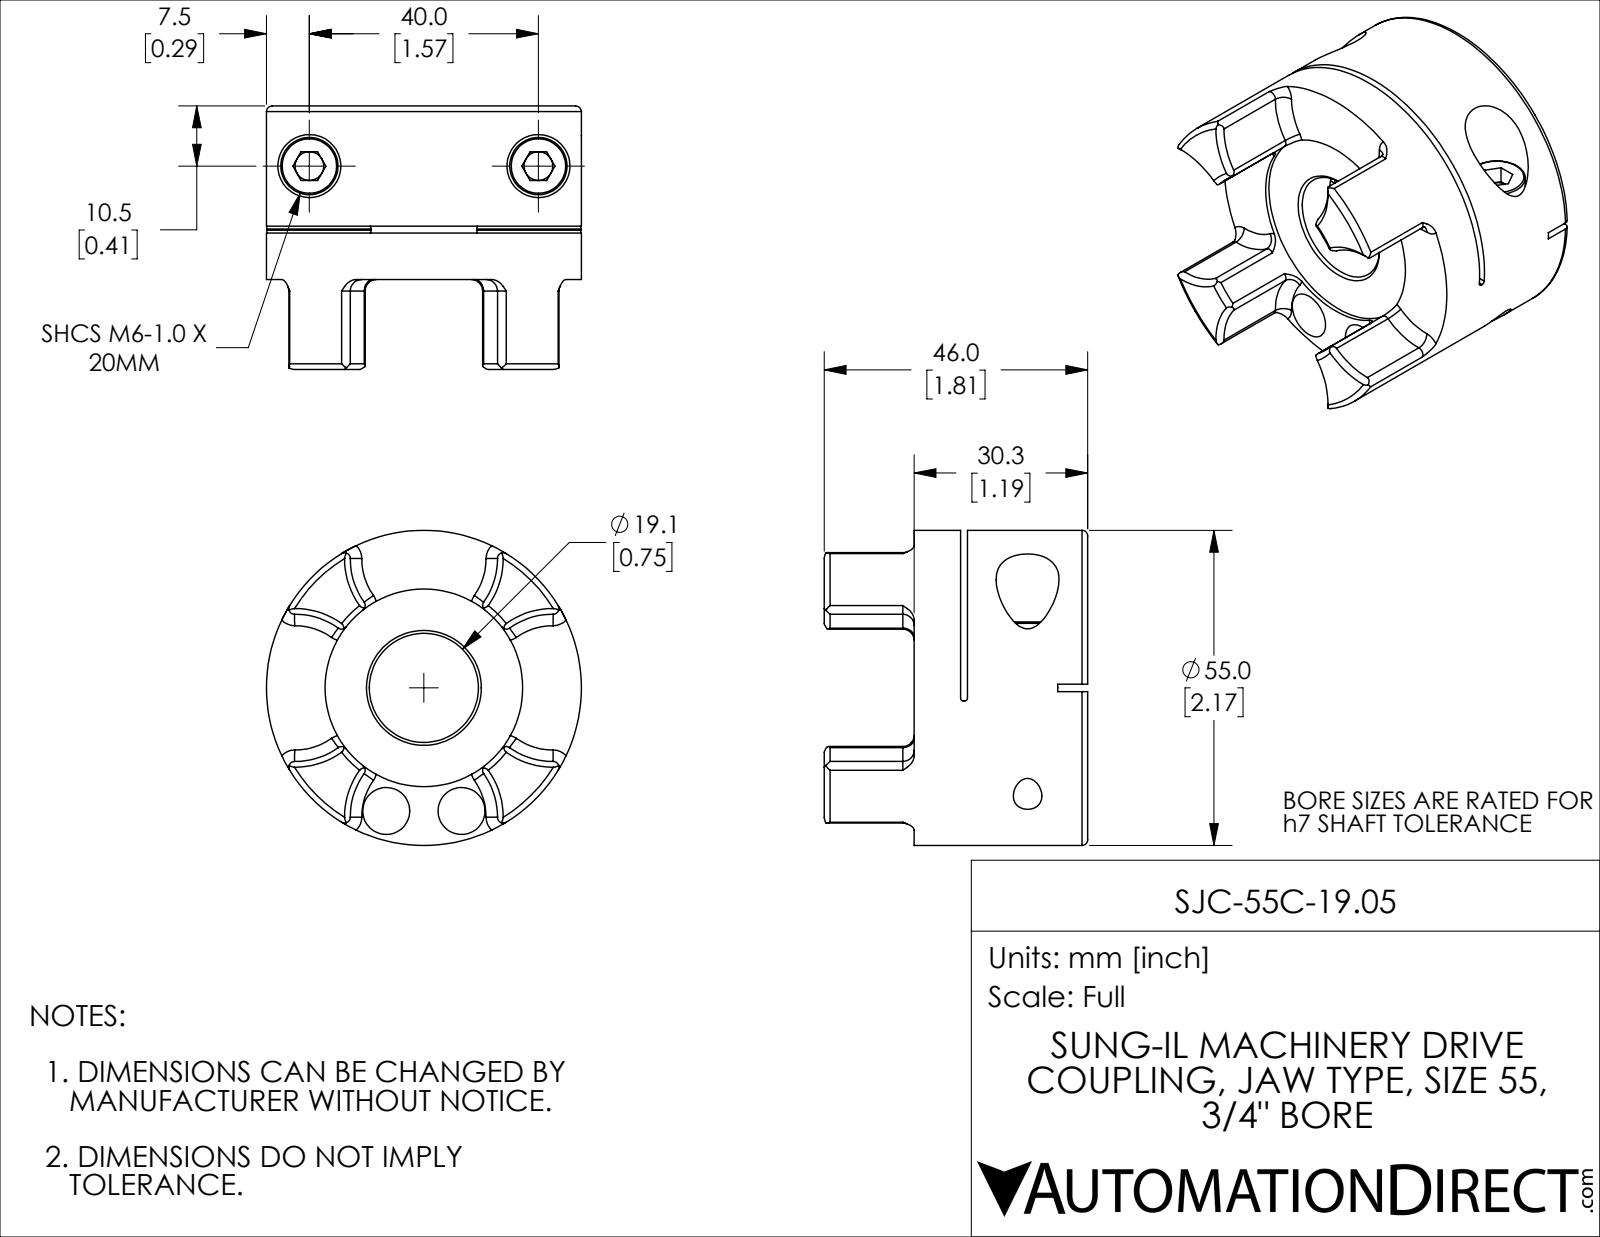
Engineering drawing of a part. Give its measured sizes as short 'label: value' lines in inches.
name: SJC-55C-19.05
written by: SolidWorks 2021 (CONFIG_CONTROL_DESIGN)
unit: in
bodies: 3 solids, 212 faces (52 planar, 76 cylindrical, 84 other)
size: 2.165 × 2.165 × 1.811
volume: 3.909 in³; area: 31.37 in²
holes: 2× ⌀0.197, 2× ⌀0.252, 2× ⌀0.323, 2× ⌀0.433, 1× ⌀0.75, 1× ⌀1.358
bosses: 2× ⌀0.394, 2× ⌀0.236, 1× ⌀2.165
rounds: 16× R0.039, 4× R0.506, 2× R0.02, 1× R1.969
face distances: 0.874, 0.047, 0.827, 0.319, 0.366, 1.193, 0.031, 0.287, 0.335, 1.161
hole spacings: 0.885, 0.517, 1.575
